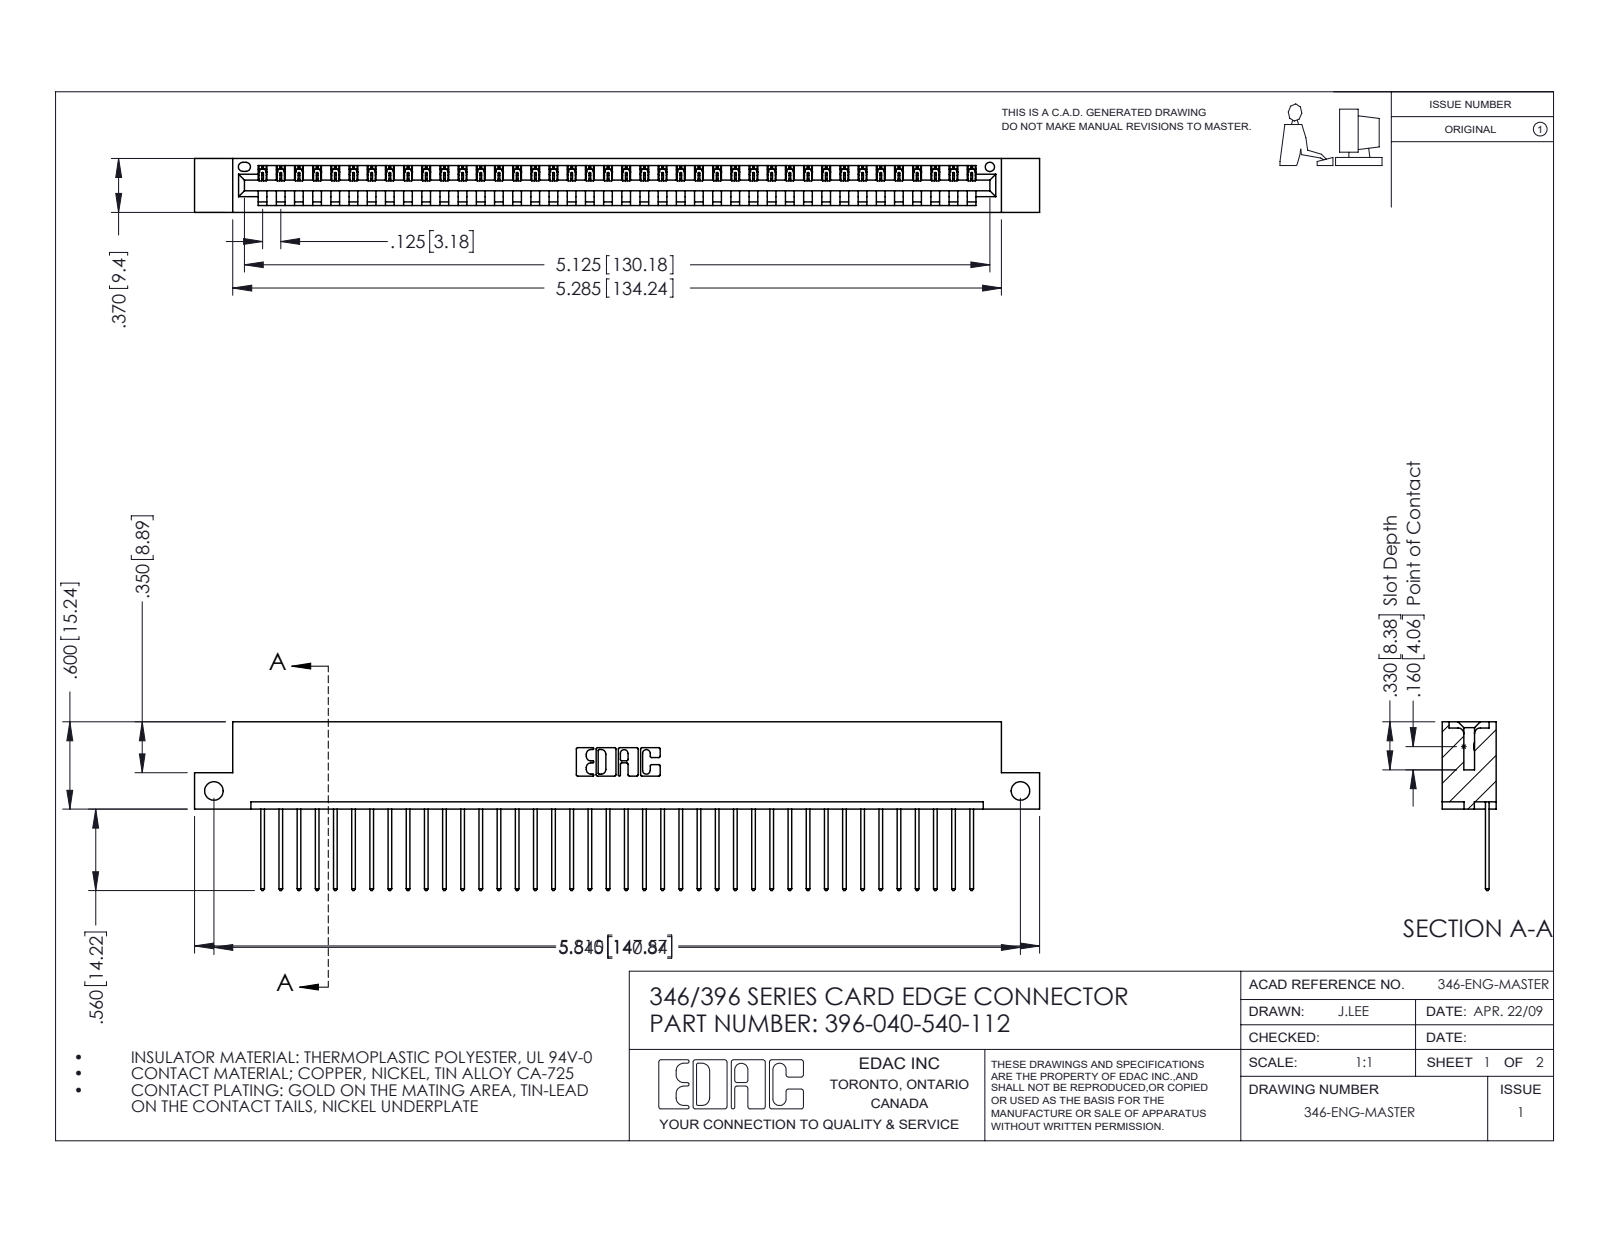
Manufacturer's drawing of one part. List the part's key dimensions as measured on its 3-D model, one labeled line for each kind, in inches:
Part name (STEP PRODUCT): 345-292-001_345-293-140; 346 Part_Flush Mounting Lugs - Side Mount; 396-040-540-112
STEP written by: SolidWorks 2016 (CONFIG_CONTROL_DESIGN)
Units: inches
Bodies: 41 solids, 2442 faces (1676 planar, 766 cylindrical, 0 other)
Overall size (bounding box): 5.81 × 1.16 × 0.37
Volume: 0.859 in³ · Surface area: 27.63 in²
Round holes (diameter × count): ⌀0.128 ×2, ⌀0.064 ×1
Partial cylindrical surfaces — rounded edges, fillets, slot ends (radius × count): R0.006 ×80, R0.01 ×80, R0.01 ×22, R0.007 ×6, R0.031 ×6, R0.026 ×3, R0.031 ×2, R0.04 ×2
Main face-to-face distances: 0.048, 0.322, 0.37, 0.25, 0.072, 0.298, 0.025, 0.148, 0.222, 0.1
Hole centre spacings: 5.545
